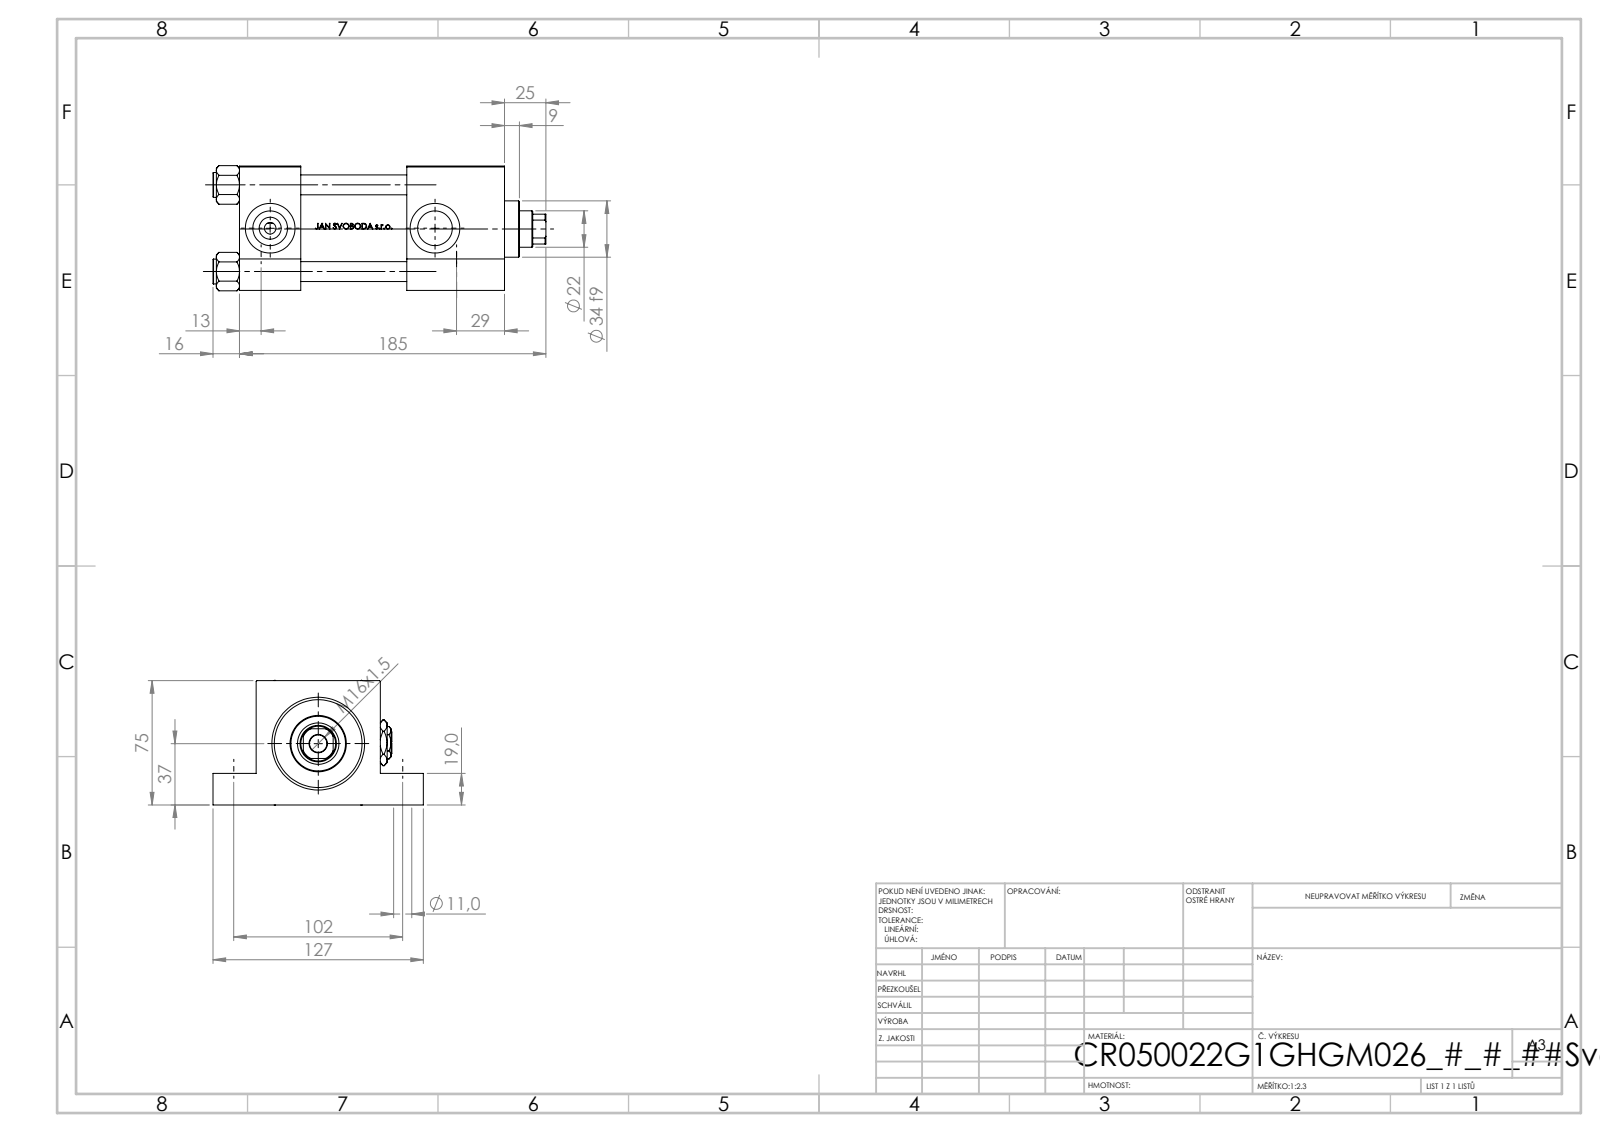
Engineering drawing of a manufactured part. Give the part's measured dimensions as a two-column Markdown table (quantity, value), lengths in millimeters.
| quantity | value |
| --- | --- |
| part name | V215_VC_A; V215CR_G_Body; V215CR_G_TYCINKA; V215CR_VCP_G (+2 more) |
| STEP written by | SolidWorks 2019 (CONFIG_CONTROL_DESIGN) |
| units | millimeters |
| bodies | 12 solids, 1134 faces (454 planar, 128 cylindrical, 552 other) |
| overall size | 201 × 127 × 75.54 |
| volume | 760 395 mm³ |
| surface area | 164 621 mm² |
| round holes (diameter × count) | 11 × 4, 12 × 4, 7 × 2, 20.96 × 2, 30 × 2, 10.5 × 1, 22 × 1, 25 × 1, 41 × 1, 50 × 1, 53 × 1 |
| round bosses / shafts (diameter × count) | 15 × 4, 56 × 1, 34 × 1 |
| partial cylindrical surfaces (radius × count) | 10.5 × 1 |
| main face-to-face distances | 75, 101, 37, 160, 123, 26, 19, 56, 64, 59 |
| hole center spacings | 52.3, 36.63, 37.34, 73.96, 102, 118, 155.97, 99.5 |
